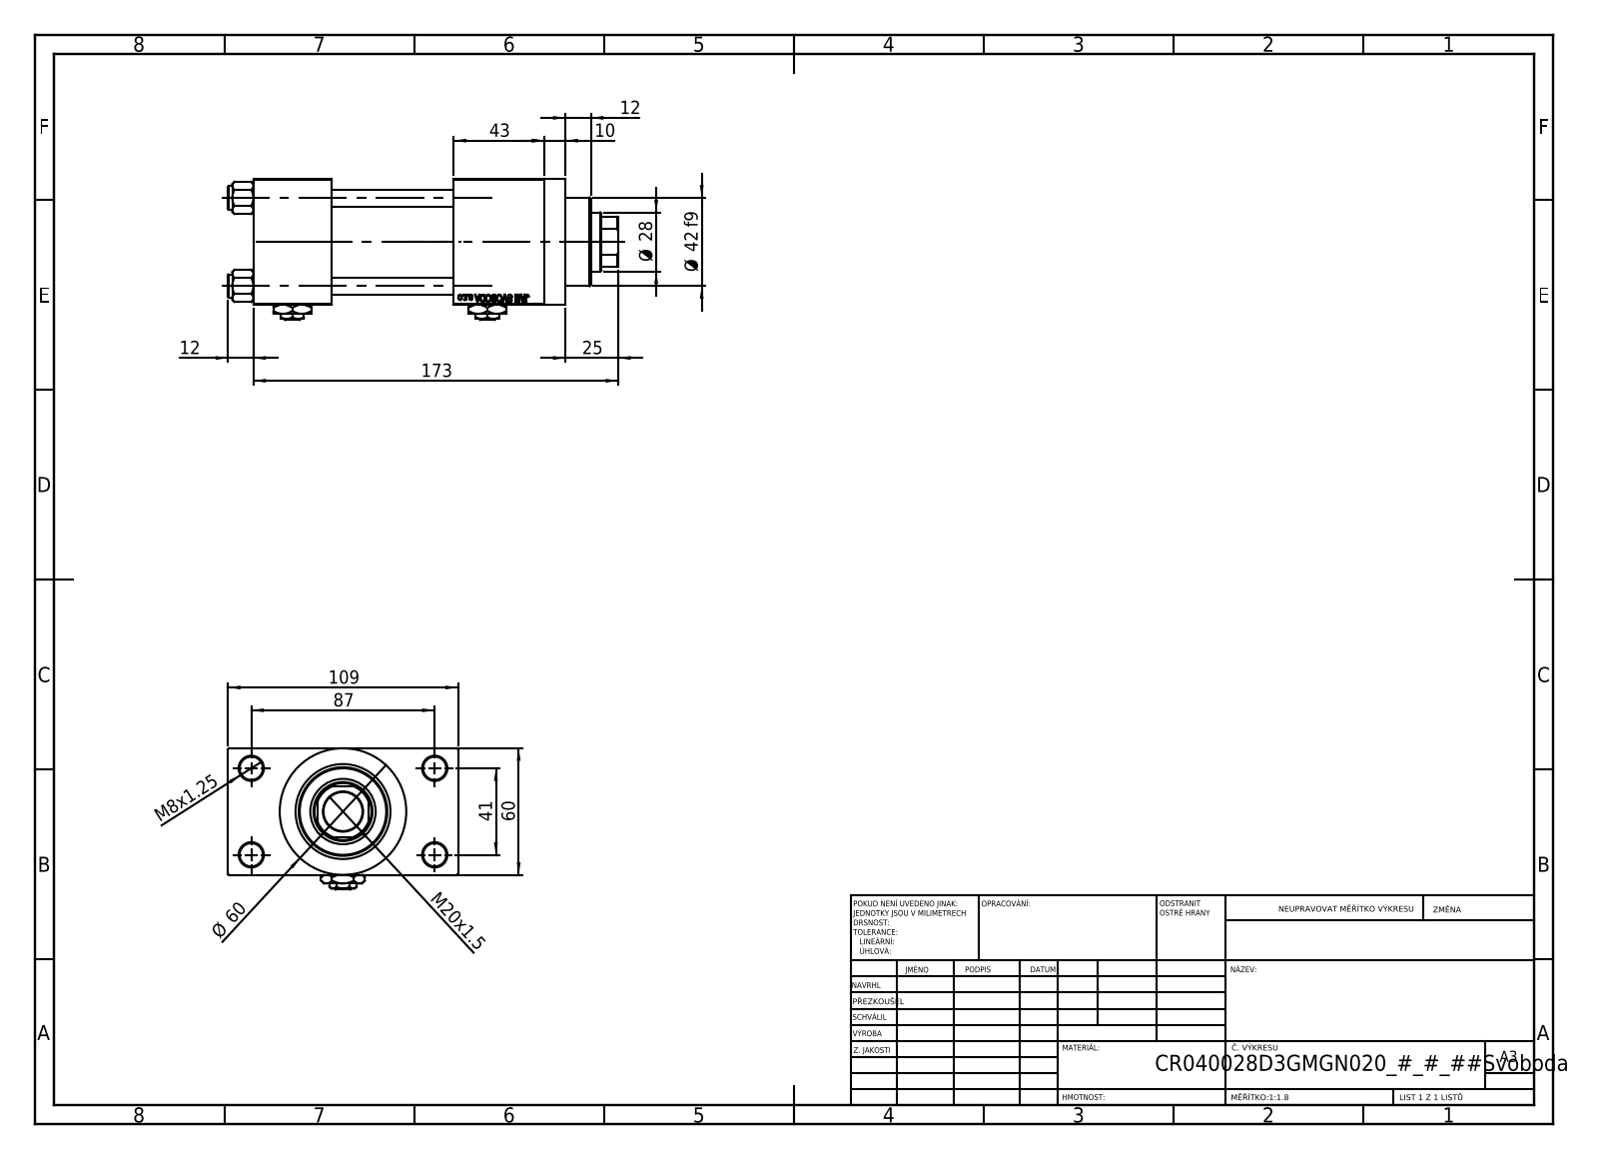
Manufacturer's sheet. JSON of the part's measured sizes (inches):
{"part_name": "NUT_M5_D; V215CR_D_Body; V215CR_VCP_D; V215CR_D_TYCINKA (+2 more)", "step_written_by": "SolidWorks 2019 (CONFIG_CONTROL_DESIGN)", "units": "inches", "bodies": {"solids": 13, "faces": 1205, "planar": 546, "cylindrical": 99, "other": 560}, "overall_size": [7.283, 4.291, 2.638], "volume_in3": 32.16, "surface_area_in2": 204.1, "round_holes": [[0.315, 4], [0.433, 4], [0.656, 4], [0.945, 4], [0.276, 3], [0.728, 1], [1.102, 1], [1.22, 1], [1.575, 1], [1.772, 1]], "round_bosses_or_shafts": [[0.433, 4], [2.362, 1], [1.811, 1], [1.654, 1]], "partial_cylinders_radius": [[0.531, 1]], "face_to_face_distances": [2.362, 2.283, 0.965, 3.327, 1.457, 3.74, 5.433, 3.976, 1.693, 4.291], "hole_center_spacings": [0.892, 1.161, 1.642, 1.856, 1.893, 2.533, 3.011, 1.614]}
